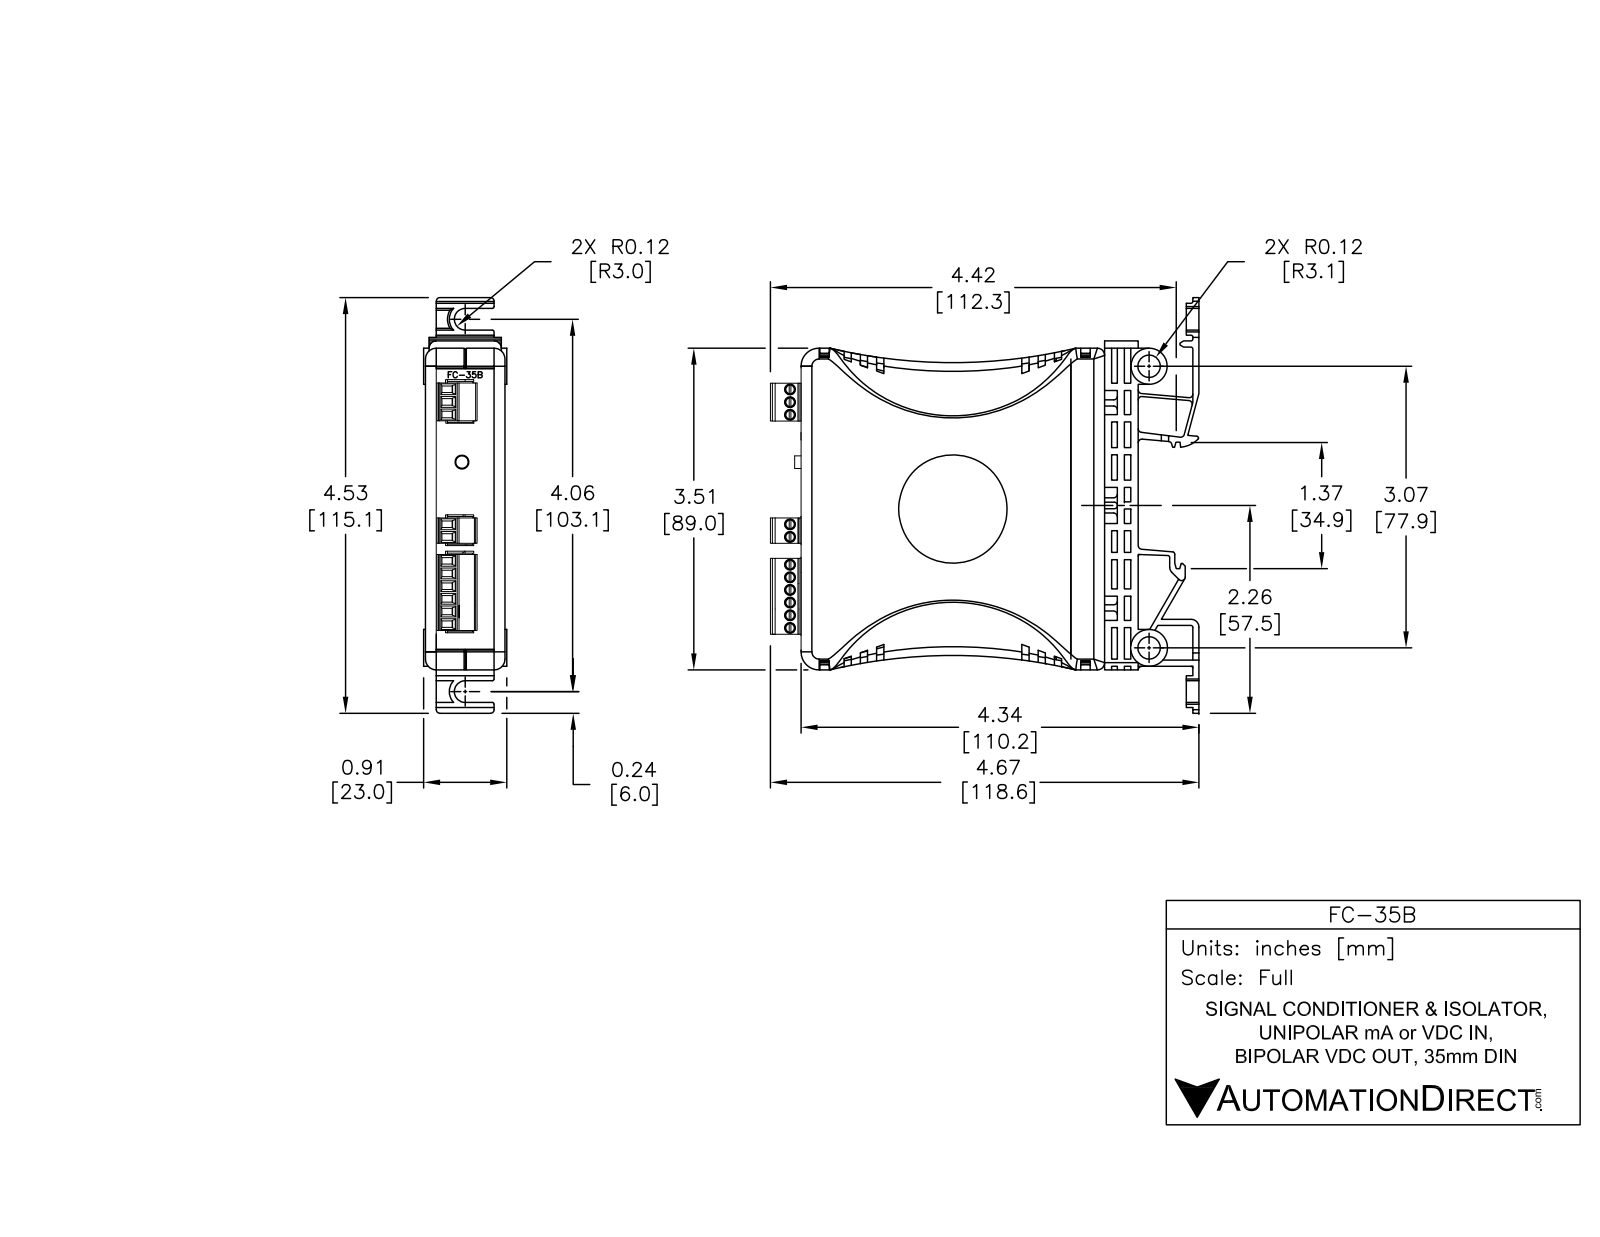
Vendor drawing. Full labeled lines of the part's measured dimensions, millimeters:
Part name (STEP PRODUCT): FC-35B
STEP written by: SolidWorks 2019 (CONFIG_CONTROL_DESIGN)
Units: millimetres
Bodies: 8 solids, 3636 faces (2011 planar, 392 cylindrical, 1233 other)
Overall size (bounding box): 119.6 × 115 × 23
Volume: 57 810 mm³ · Surface area: 59 810 mm²
Round holes (diameter × count): ⌀0.4 ×4, ⌀8 ×4, ⌀6.2 ×2, ⌀3.1 ×1, ⌀3.8 ×1
Round bosses / shafts (diameter × count): ⌀3.9 ×4, ⌀0.3 ×2, ⌀30 ×1, ⌀10.2 ×1, ⌀10 ×1, ⌀3.5 ×1, ⌀2.3 ×1
Partial cylindrical surfaces — rounded edges, fillets, slot ends (radius × count): R0.5 ×37, R1 ×34, R0.3 ×27, R0.4 ×16, R2 ×11, R3 ×10, R1.4 ×8, R0.2 ×7
Main face-to-face distances: 1.6, 20.4, 22, 18.8, 1, 0.6, 21, 19.4, 92.5, 3.5
Hole centre spacings: 2, 10, 14, 81, 82.2, 8, 8.1, 12
